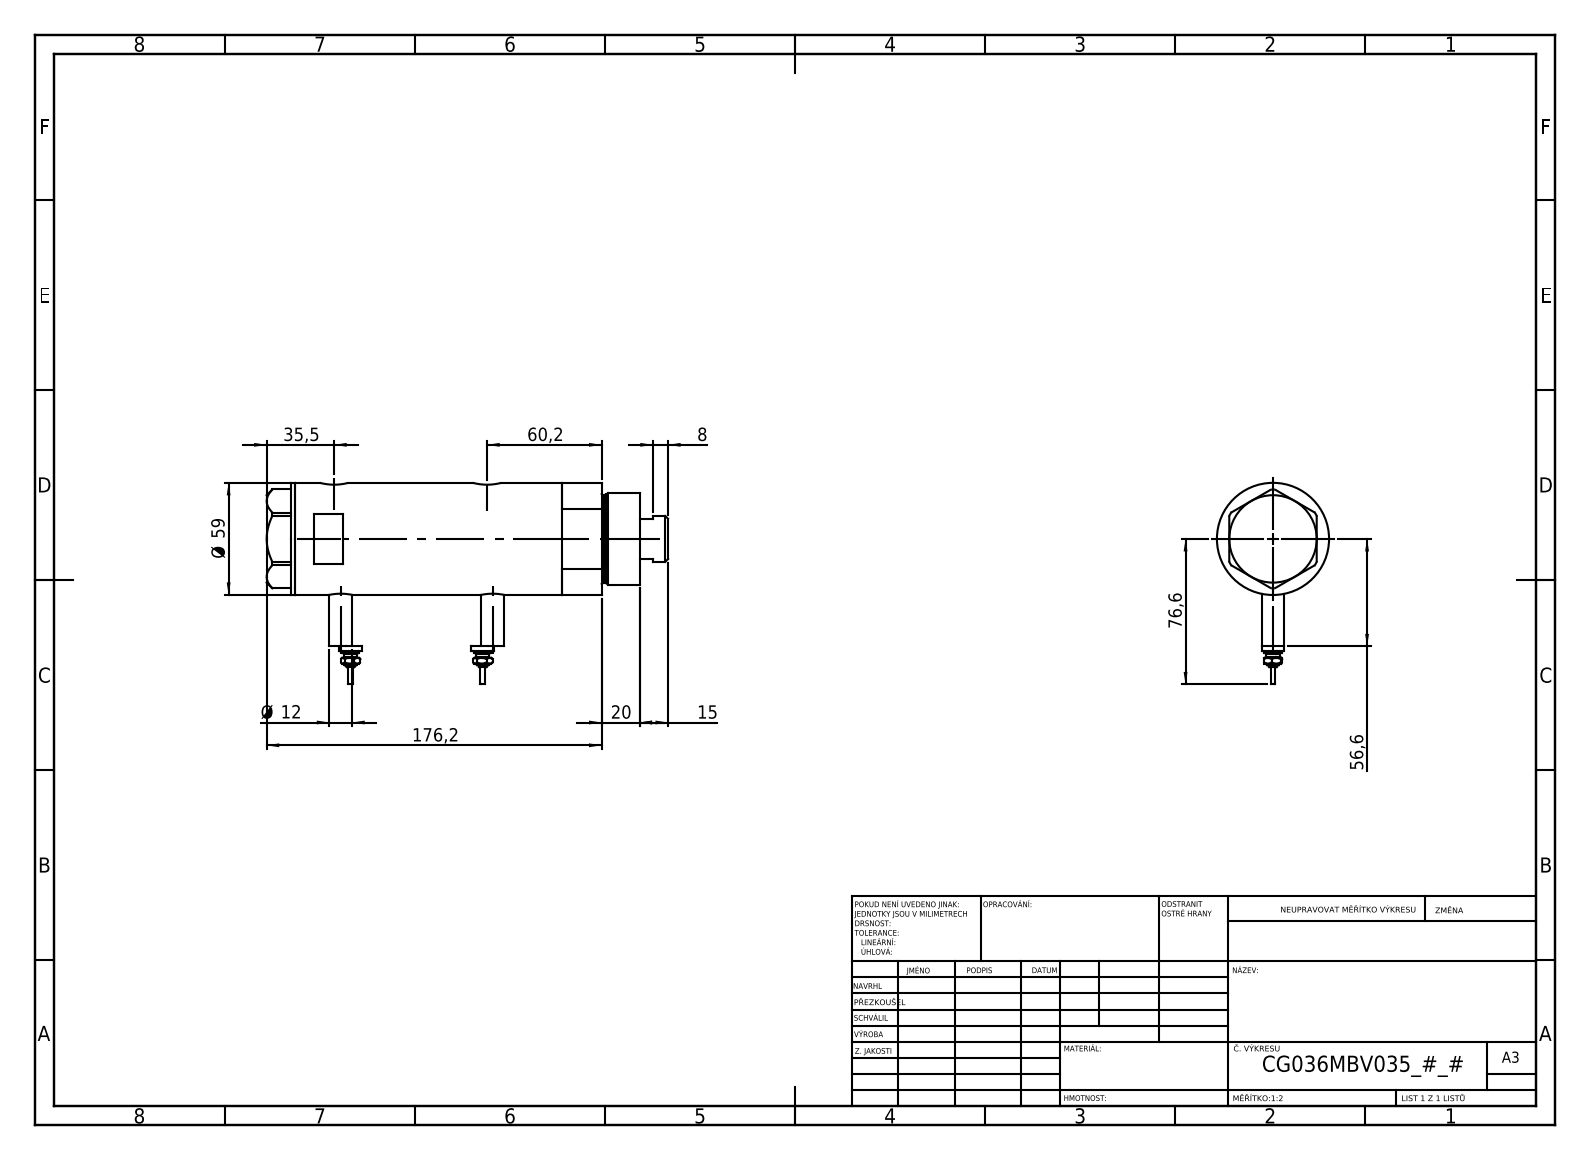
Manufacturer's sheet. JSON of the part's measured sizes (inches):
{"part_name": "V270CG_VC; V270CG_BACK; V270CG_FRONT; V270CG_MIDDLE (+1 more)", "step_written_by": "SolidWorks 2019 (CONFIG_CONTROL_DESIGN)", "units": "inches", "bodies": {"solids": 6, "faces": 212, "planar": 79, "cylindrical": 69, "other": 64}, "overall_size": [8.315, 4.177, 2.323], "volume_in3": 30.05, "surface_area_in2": 160.1, "round_holes": [[0.383, 2], [0.492, 2], [0.591, 2], [0.335, 1], [0.984, 1], [1.043, 1], [1.417, 1], [1.575, 1], [2.047, 1]], "round_bosses_or_shafts": [[0.472, 4], [0.354, 2], [0.276, 2], [0.177, 2], [0.098, 2], [2.323, 1], [1.89, 1], [1.811, 1]], "face_to_face_distances": [4.024, 0.925, 3.098, 0.591, 1.516, 4.614, 0.079, 7.724, 7.134, 6.209], "hole_center_spacings": [0.114, 0.138, 3.031, 3.146, 3.169, 3.283]}
